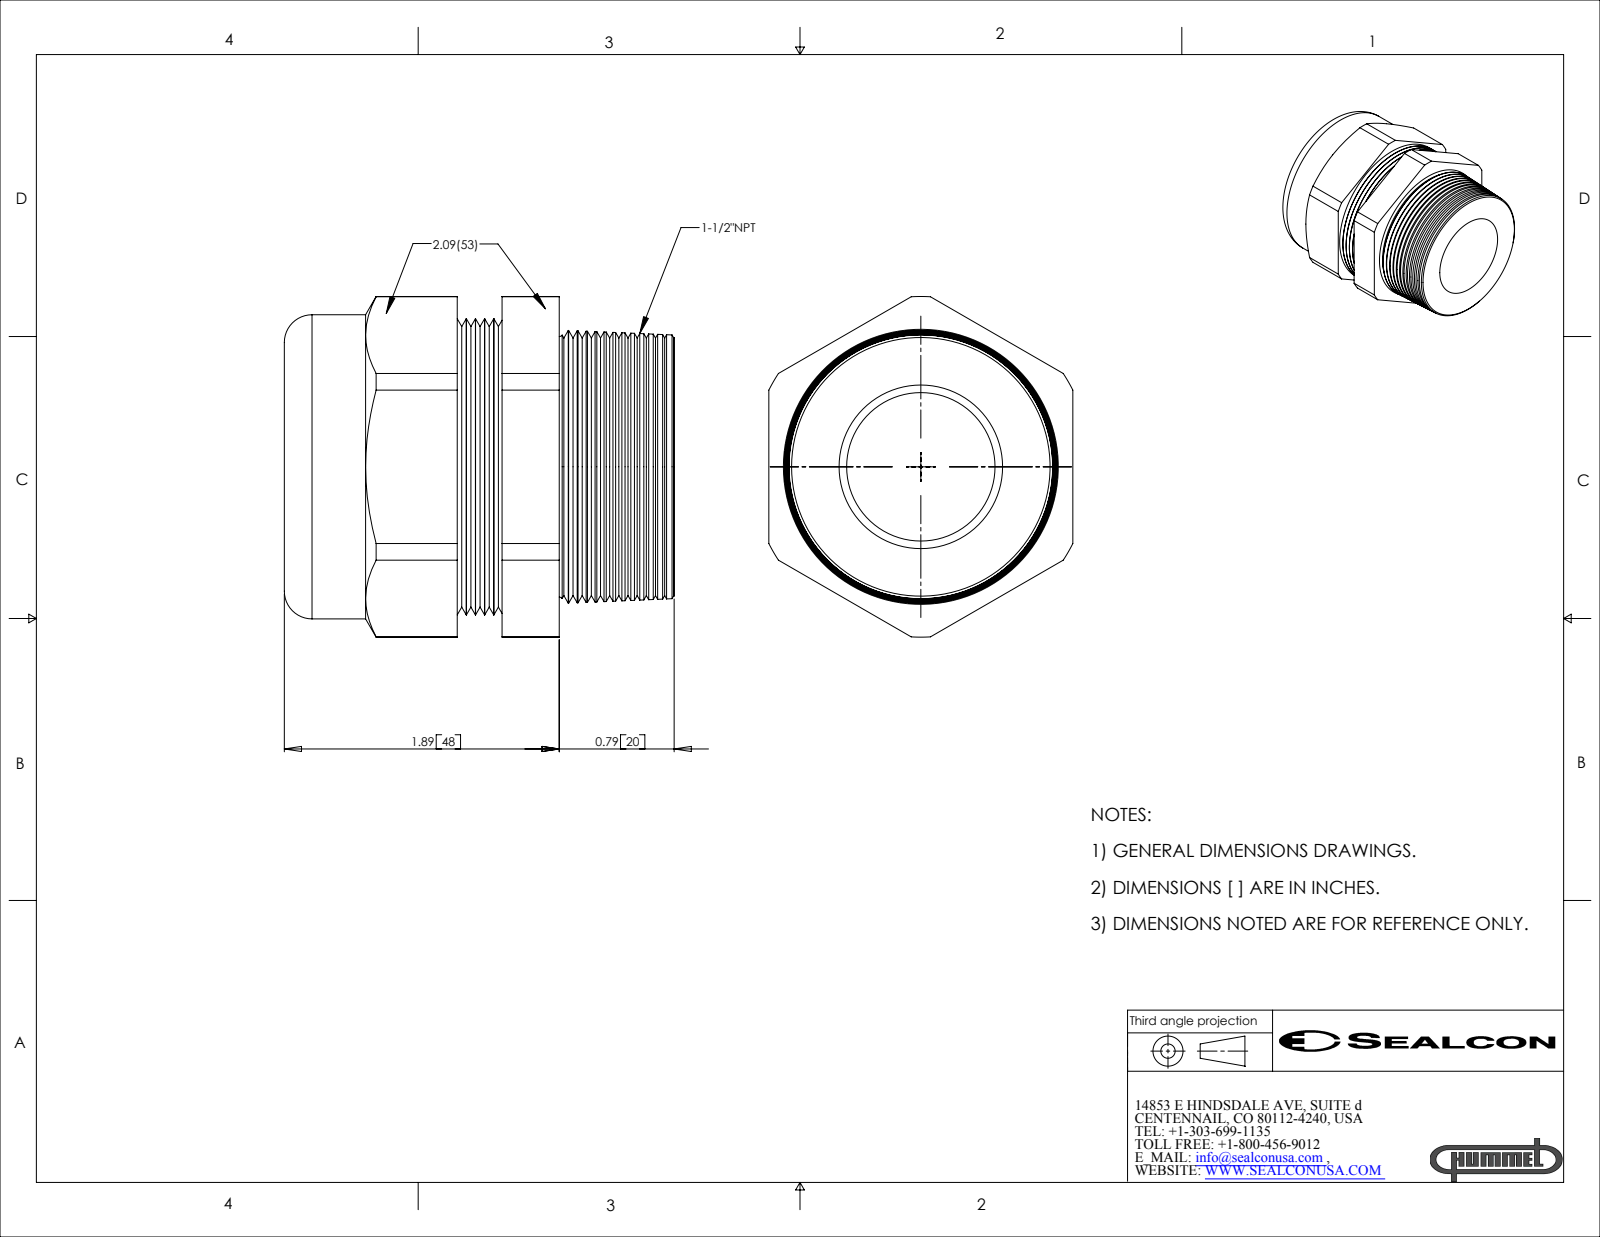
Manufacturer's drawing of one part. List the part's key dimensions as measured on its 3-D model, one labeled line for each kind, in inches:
Part name (STEP PRODUCT): CD36NR-BK
STEP written by: SolidWorks 2007 (CONFIG_CONTROL_DESIGN)
Units: inches
Bodies: 2 solids, 164 faces (20 planar, 32 cylindrical, 112 other)
Overall size (bounding box): 2.68 × 2.341 × 2.09
Volume: 6.364 in³ · Surface area: 45.22 in²
Round holes (diameter × count): ⌀1.02 ×1, ⌀1.598 ×1
Round bosses / shafts (diameter × count): ⌀2.09 ×1, ⌀2.035 ×1
Partial cylindrical surfaces — rounded edges, fillets, slot ends (radius × count): R1.17 ×1
Main face-to-face distances: 2.09, 2.121, 0.539, 2.66, 1.87, 1.331, 0.79, 1.477, 0.938, 0.393
